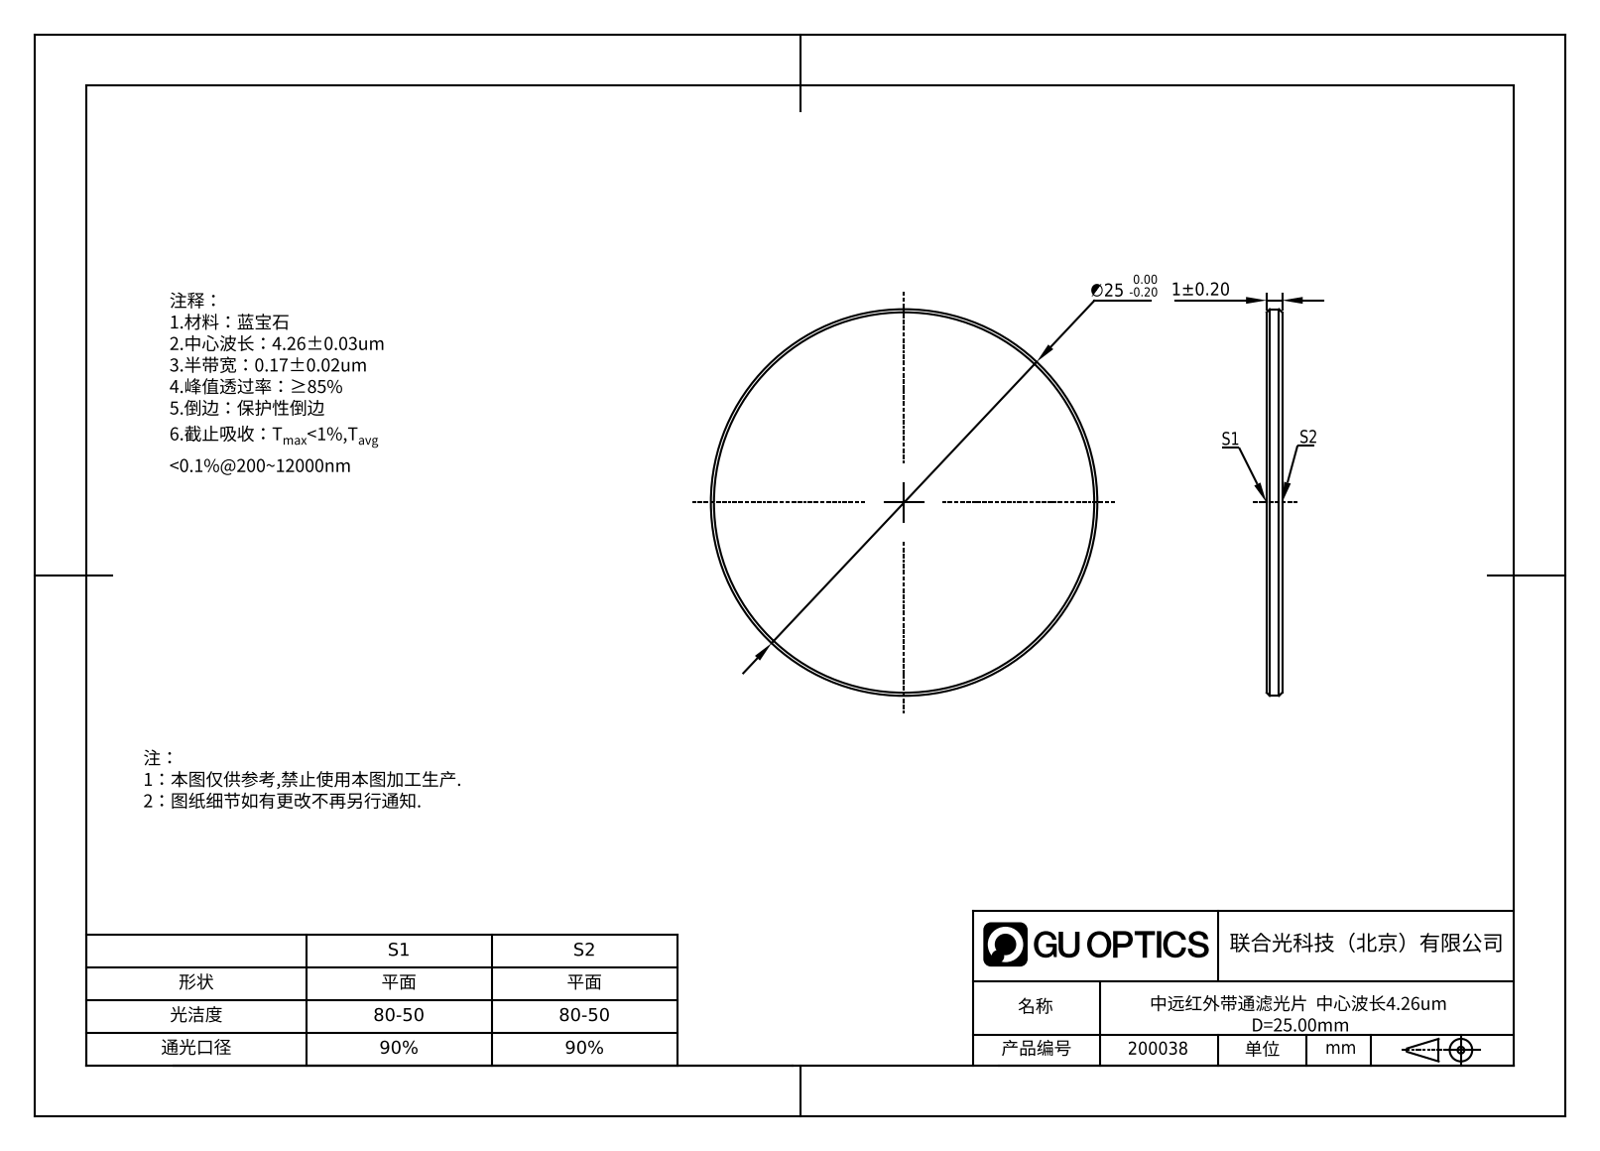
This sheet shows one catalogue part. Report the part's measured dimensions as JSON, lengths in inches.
{"part_name": "GNIF-170-4260-D25", "step_written_by": "SolidWorks 2022 (AUTOMOTIVE_DESIGN)", "units": "inches", "bodies": {"solids": 1, "faces": 8, "planar": 2, "cylindrical": 2, "other": 4}, "overall_size": [0.984, 0.984, 0.039], "volume_in3": 0.03, "surface_area_in2": 1.615, "round_bosses_or_shafts": [[0.984, 1]], "face_to_face_distances": [0.039]}
